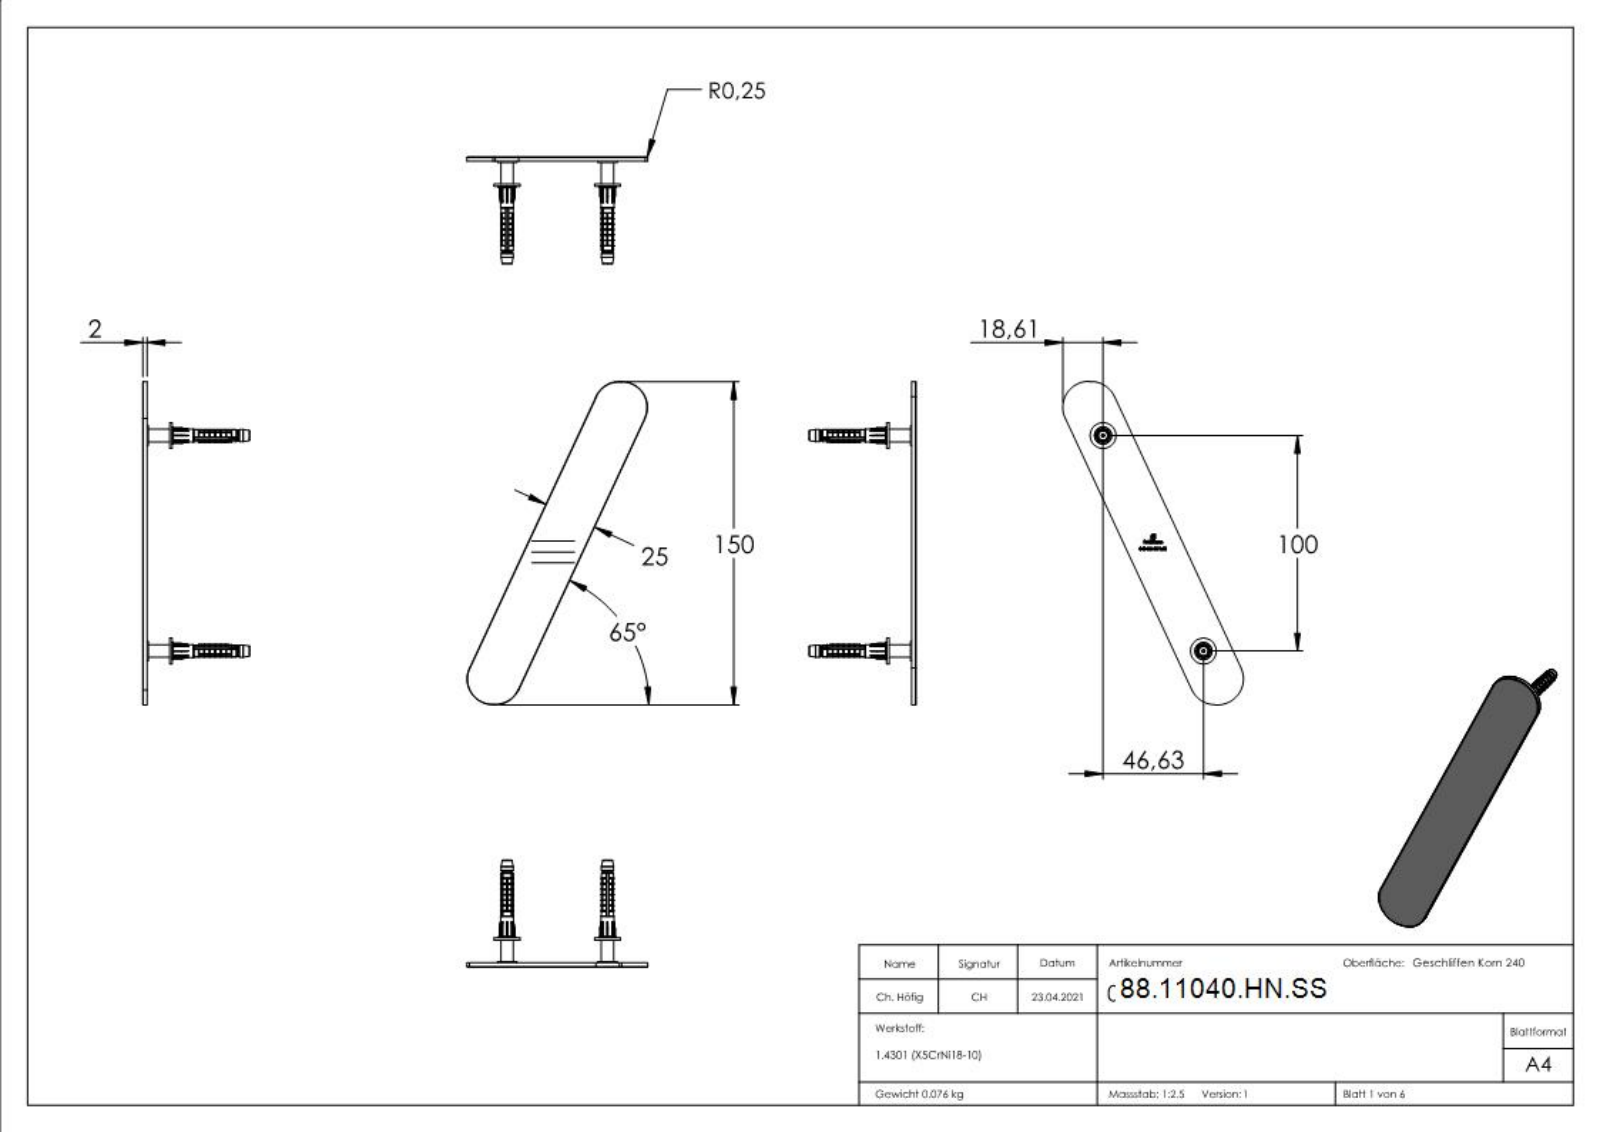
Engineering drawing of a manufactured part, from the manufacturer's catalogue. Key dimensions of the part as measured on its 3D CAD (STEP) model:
Part name (STEP PRODUCT): 040-HN-X Teil1; 040-HN-SS; 040-HN-X Teil2_040-HN-X Teil2; 040-HN-X Teil4 (+5 more)
STEP written by: SolidWorks 2018 (CONFIG_CONTROL_DESIGN)
Units: millimetres
Bodies: 7 solids, 1662 faces (413 planar, 387 cylindrical, 862 other)
Overall size (bounding box): 10000 × 5217.43 × 4607.88
Volume: 10 589 mm³ · Surface area: 12 999 mm²
Round holes (diameter × count): ⌀3.3 ×2, ⌀4.3 ×2
Round bosses / shafts (diameter × count): ⌀12 ×2, ⌀9 ×2, ⌀8 ×2, ⌀6 ×2, ⌀5.8 ×2, ⌀5.6 ×2, ⌀4.6 ×2, ⌀4 ×2
Partial cylindrical surfaces — rounded edges, fillets, slot ends (radius × count): R0.1 ×24, R0.25 ×4, R12 ×4, R3.5 ×2
Main face-to-face distances: 2, 11.6, 13.6, 25, 1.1, 10.5, 12.5, 1, 0.5, 10
Hole centre spacings: 110.34
